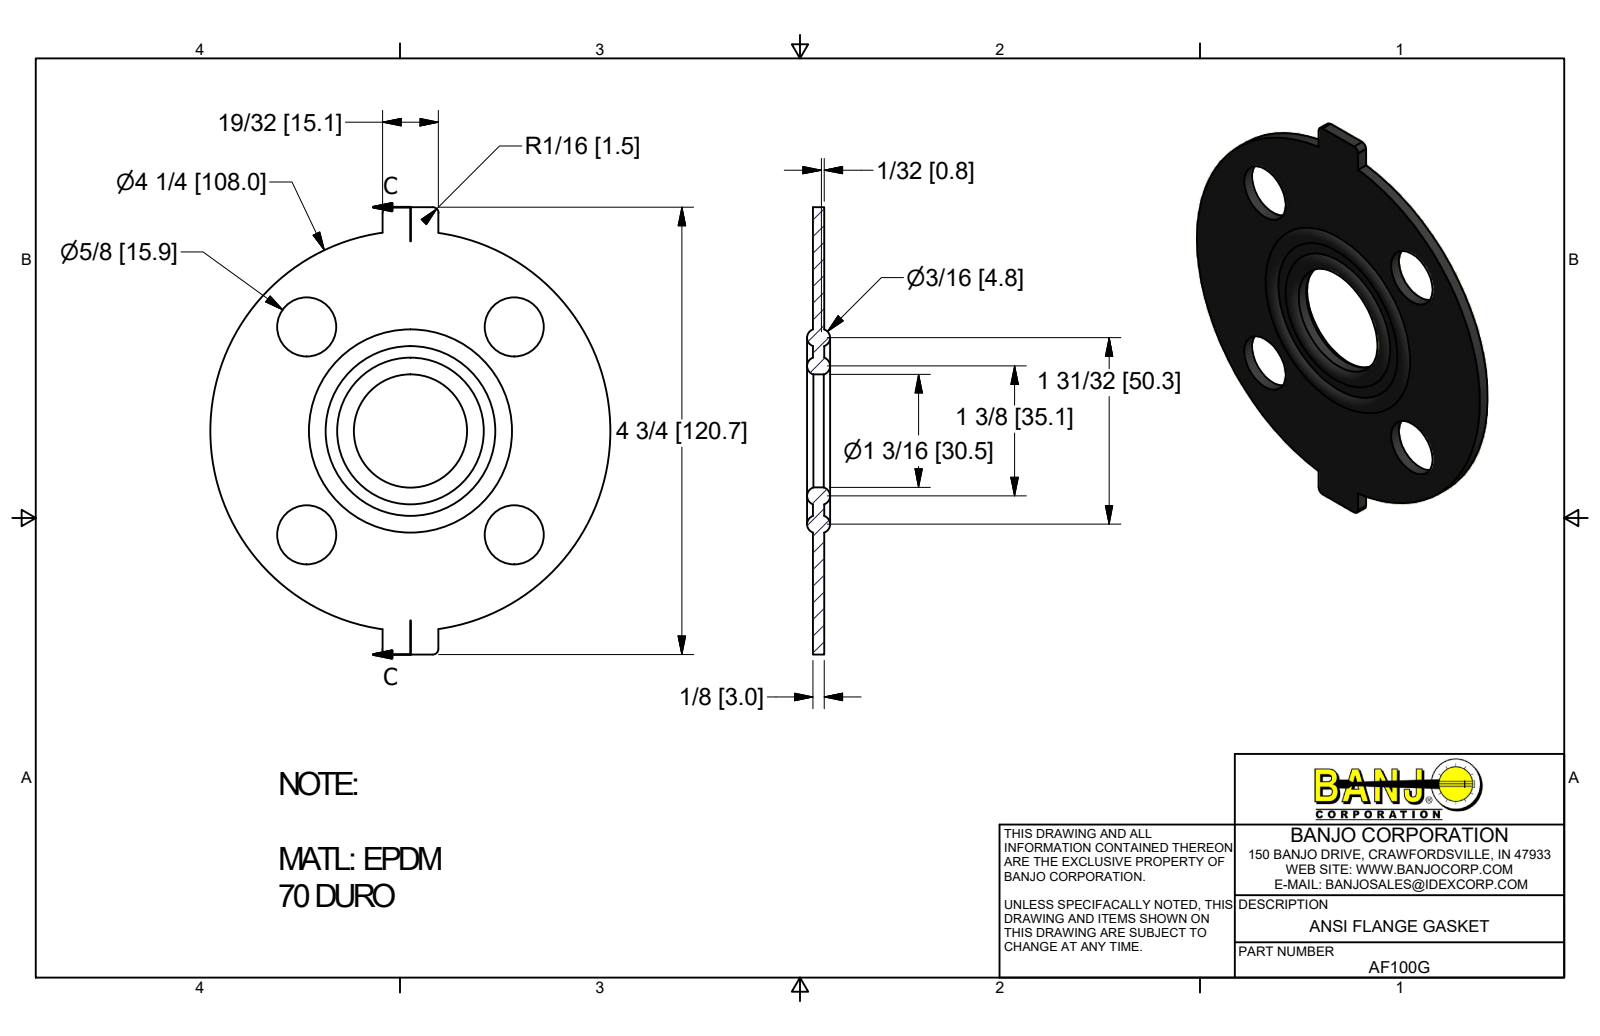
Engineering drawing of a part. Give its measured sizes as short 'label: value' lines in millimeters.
name: AF100G
written by: Autodesk Inventor 2017 (AUTOMOTIVE_DESIGN)
unit: mm
bodies: 1 solid, 25 faces (10 planar, 11 cylindrical, 4 other)
size: 120.65 × 107.95 × 6.24
volume: 26 319 mm³; area: 18 383 mm²
holes: 4× ⌀15.88, 1× ⌀30.48
bosses: 1× ⌀107.95
rounds: 4× R1.52
face distances: 3, 120.64, 15.08
hole spacings: 39.63, 56.04, 79.25
